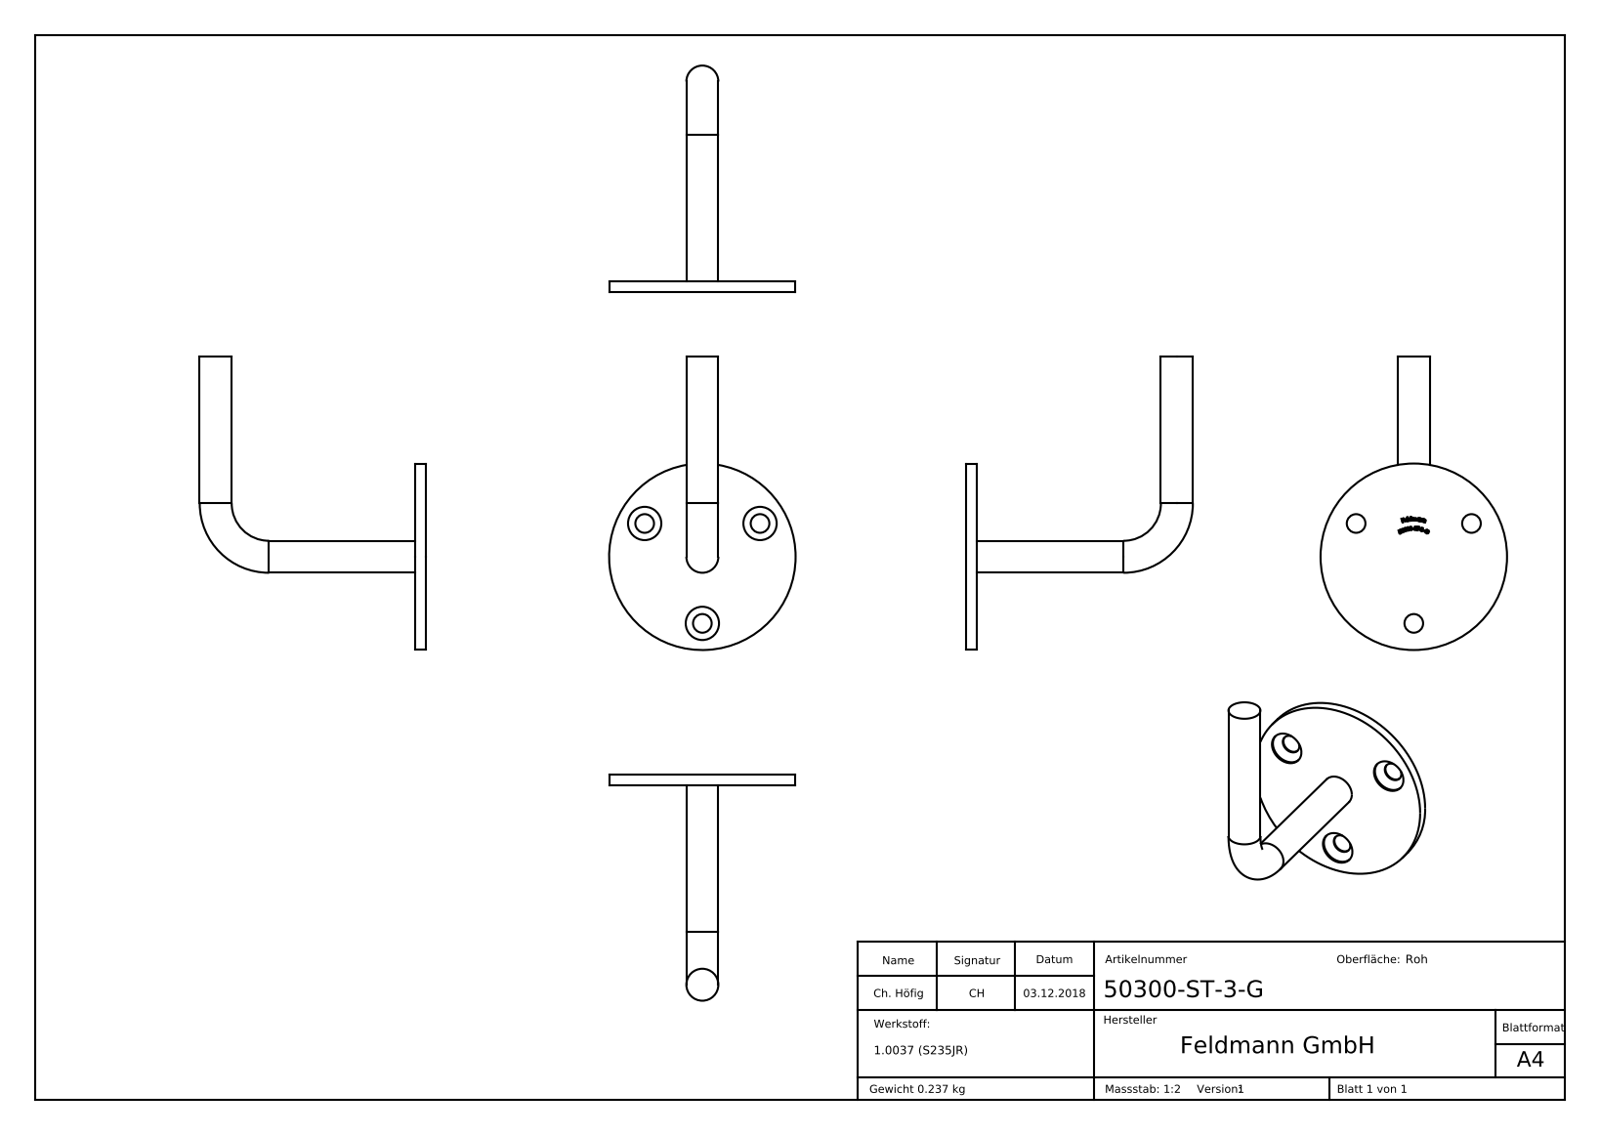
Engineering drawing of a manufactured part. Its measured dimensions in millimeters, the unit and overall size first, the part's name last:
Units: millimetres
Overall size (bounding box): 110 × 85 × 70
Round holes (diameter × count): ⌀7 ×3, ⌀12.5 ×3
Round bosses / shafts (diameter × count): ⌀12 ×2, ⌀70 ×1
Main face-to-face distances: 4, 0.5, 3.5, 0.54, 0.67, 0.72, 1.33, 0.79, 0.66, 0.6
Hole centre spacings: 43.3
Volume: 30 418 mm³ · Surface area: 13 956 mm²
Bodies: 1 solid, 282 faces (121 planar, 18 cylindrical, 143 other)
Part name (STEP PRODUCT): 50300-ST-3-G
STEP written by: SolidWorks 2015 (CONFIG_CONTROL_DESIGN)
